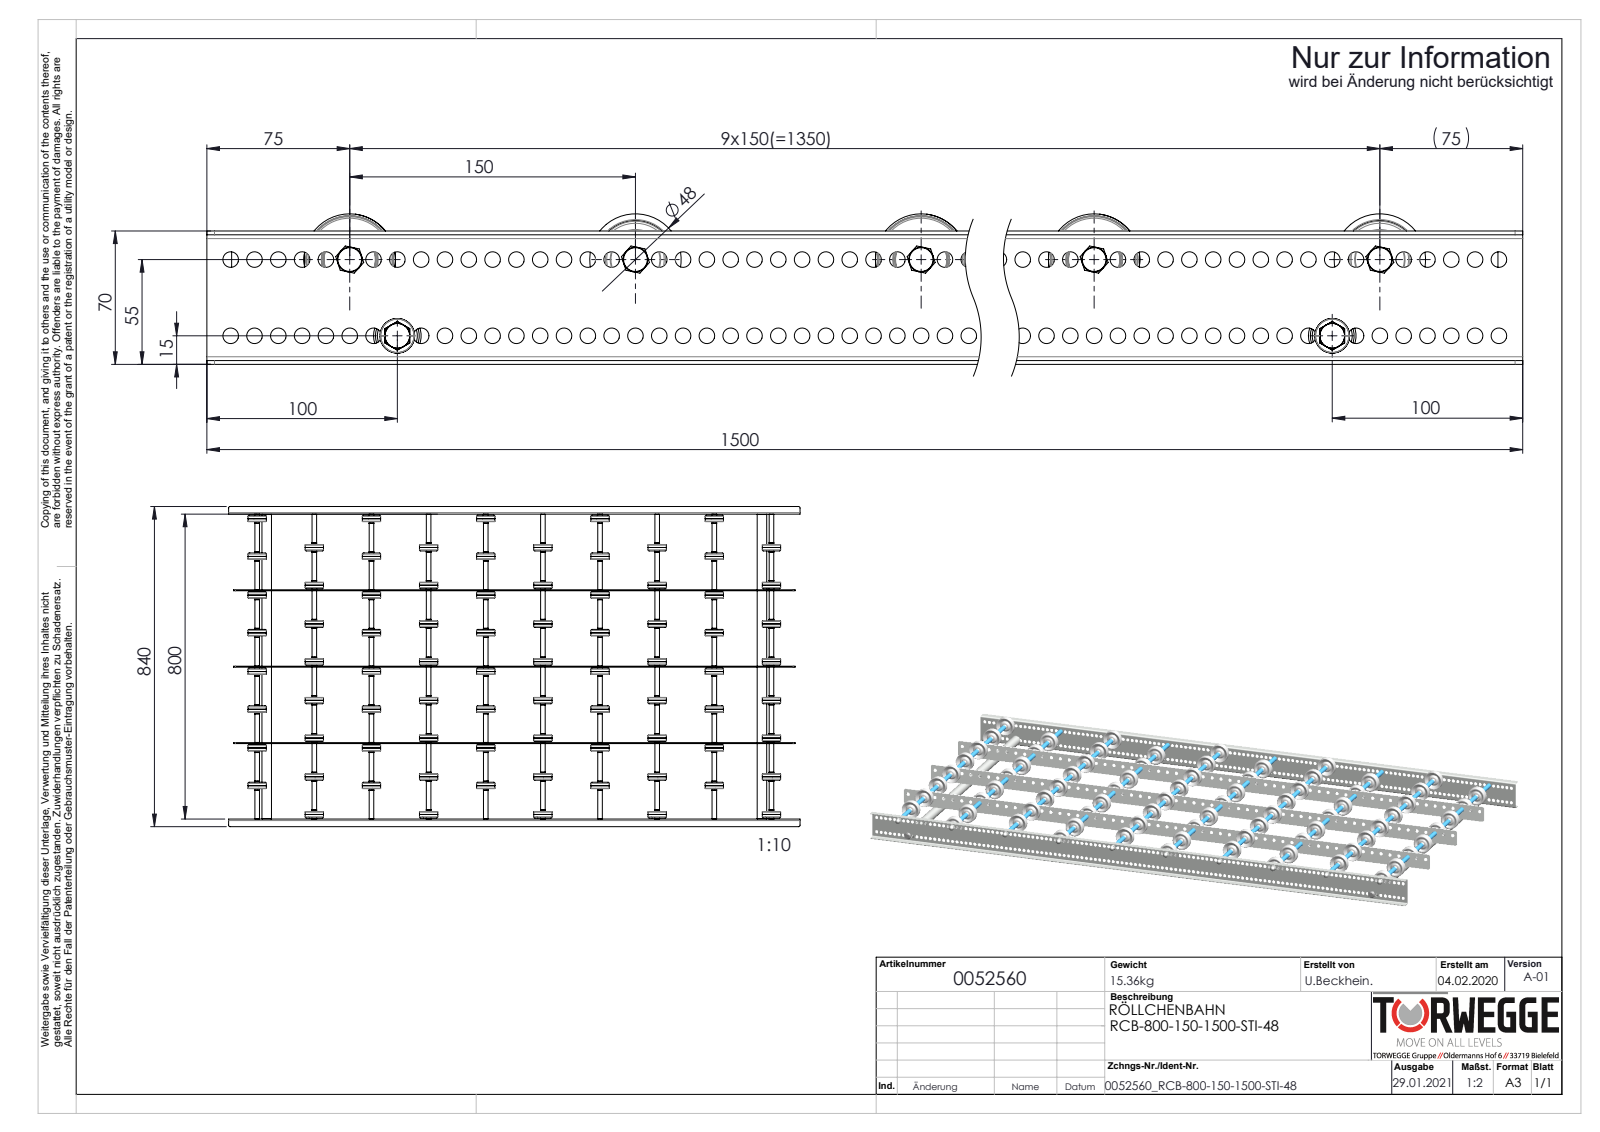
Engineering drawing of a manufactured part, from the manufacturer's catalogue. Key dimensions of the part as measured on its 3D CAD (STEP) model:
Part name (STEP PRODUCT): S100100_Längstraverse-42x2,5_S100102_Lngstraverse-RB-L1500; Röllchenachse-für-Konfiguration_EL800 Stahl; K0011528_2200-48-8; Hutmutter_DIN_1587_M8 (+6 more)
STEP written by: SolidWorks 2020 (AUTOMOTIVE_DESIGN)
Units: millimetres
Bodies: 285 solids, 9136 faces (1758 planar, 3874 cylindrical, 3504 other)
Overall size (bounding box): 1500 × 840 × 79
Volume: 3 615 000 mm³ · Surface area: 2 856 000 mm²
Round holes (diameter × count): ⌀8.2 ×238, ⌀8.5 ×59, ⌀6.65 ×10, ⌀8 ×10, ⌀9.65 ×10, ⌀15 ×10, ⌀41 ×10, ⌀6.8 ×2, ⌀21 ×2
Round bosses / shafts (diameter × count): ⌀48 ×10, ⌀13 ×10, ⌀12.5 ×10, ⌀12.4 ×10, ⌀12 ×10, ⌀11.5 ×10, ⌀25 ×2, ⌀8 ×2
Partial cylindrical surfaces — rounded edges, fillets, slot ends (radius × count): R4 ×8, R2 ×4, R5 ×4
Main face-to-face distances: 200.5, 401, 2, 203, 2.5, 198, 802, 601.5, 403.5, 398.5
Hole centre spacings: 12.5, 25, 37.5, 50, 62.5, 75, 87.5, 100
